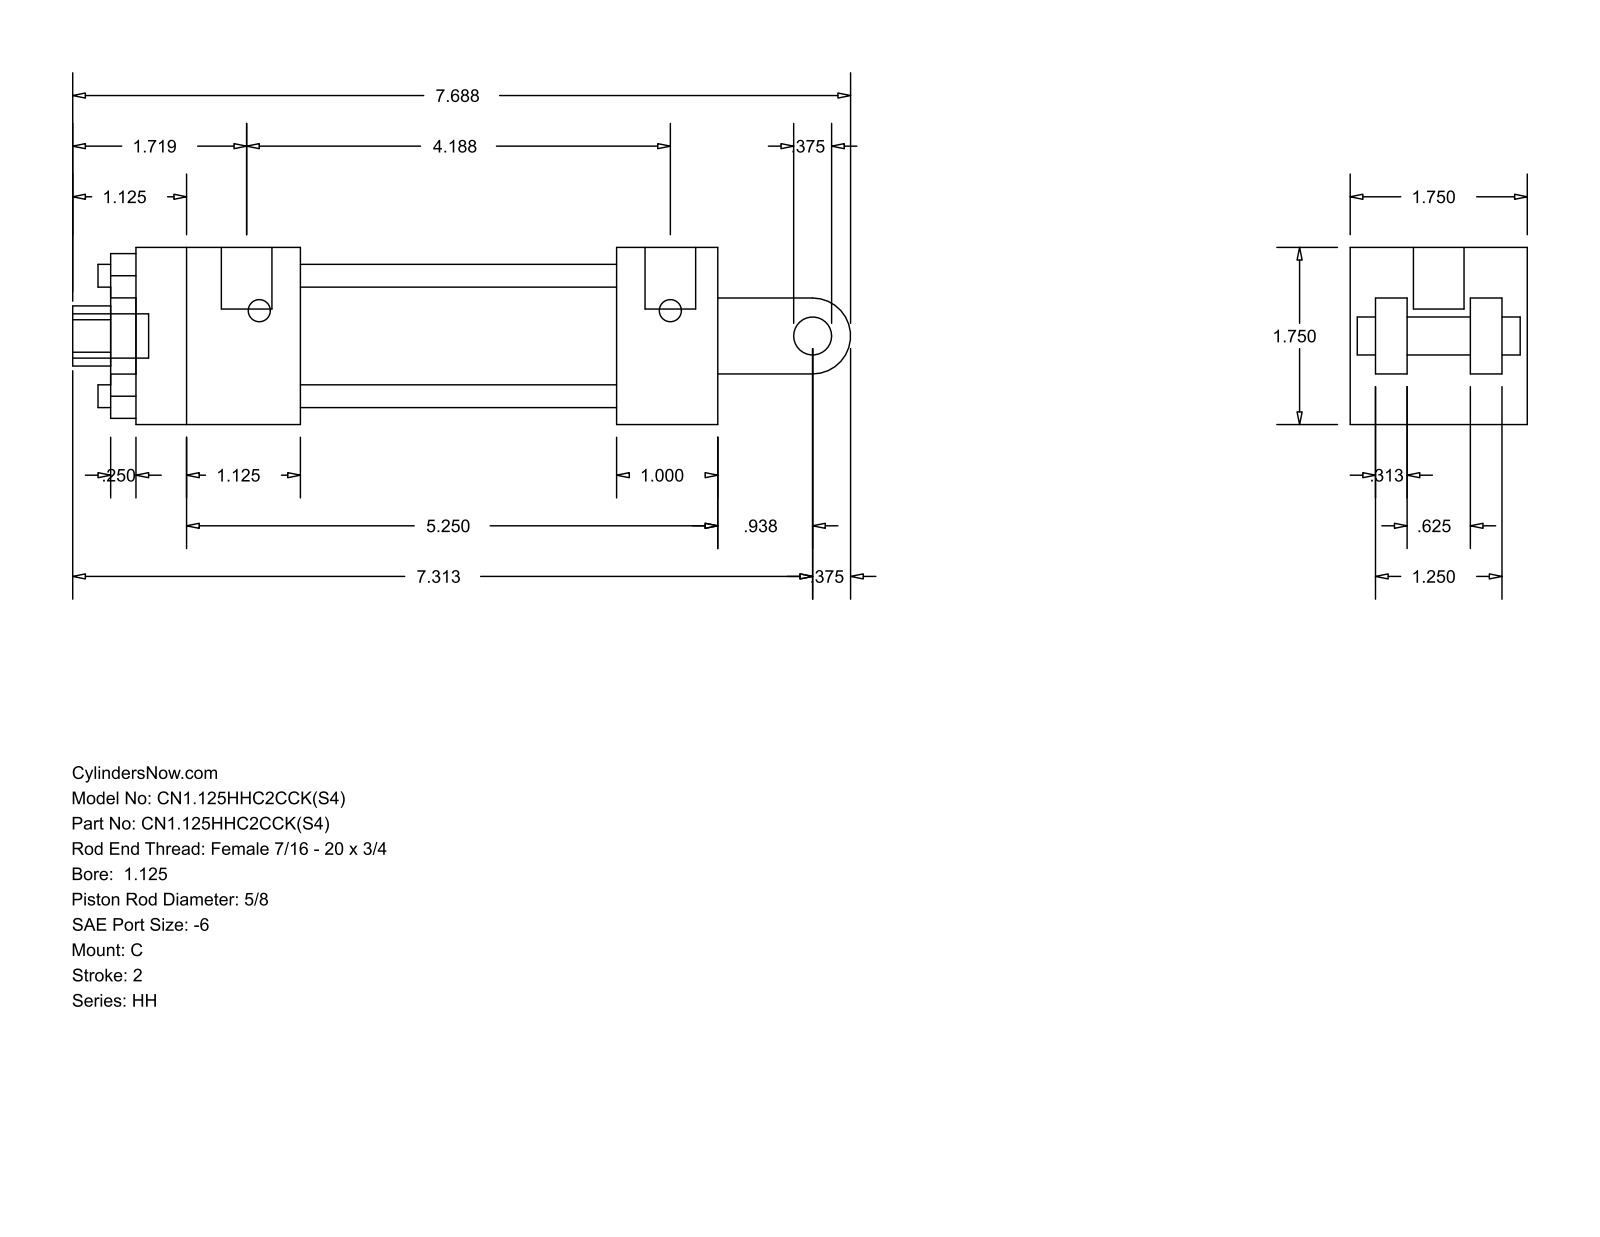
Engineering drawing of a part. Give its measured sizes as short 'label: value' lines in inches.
name: HH_C__0112_0.625
written by: GSSL Pune (CONFIG_CONTROL_DESIGN)
unit: in
bodies: 0 solids, 99 faces (70 planar, 29 cylindrical, 0 other)
size: 7.687 × 1.75 × 1.75
holes: 4× ⌀0.225, 2× ⌀0.219, 1× ⌀0.5, 1× ⌀0.625, 1× ⌀1.125, 1× ⌀1.375
bosses: 2× ⌀0.219, 1× ⌀0.5, 1× ⌀0.437, 1× ⌀0.375
rounds: 1× R0.297, 1× R0.375
face distances: 1.75, 0.25, 1.25, 0.563, 0.5, 1.188, 1.5, 0.313, 0.938, 1
hole spacings: 0.841, 1.19, 1.683
